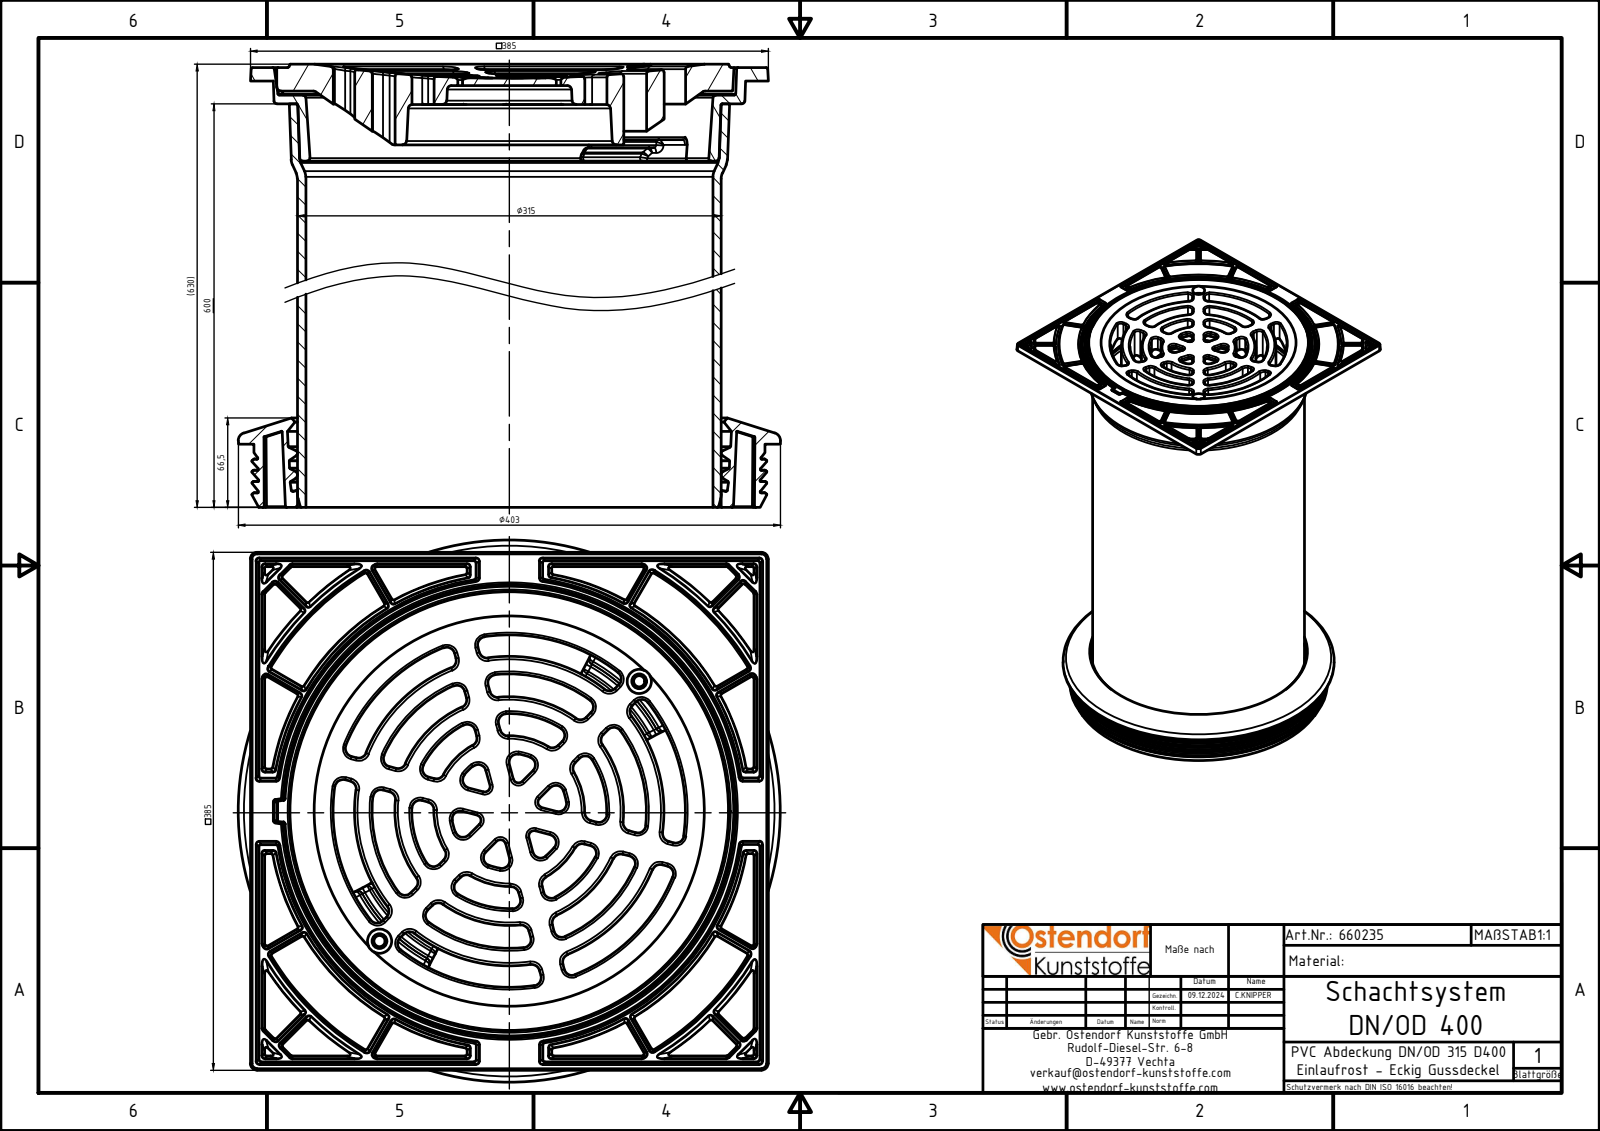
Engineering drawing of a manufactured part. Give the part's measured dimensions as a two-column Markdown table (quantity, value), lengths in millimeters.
| quantity | value |
| --- | --- |
| part name | 660235z; 660300z; 660500z; 990060z (+2 more) |
| STEP written by | Autodesk Inventor 2024 (AUTOMOTIVE_DESIGN) |
| units | millimeters |
| bodies | 4 solids, 1586 faces (235 planar, 431 cylindrical, 920 other) |
| overall size | 629.5 × 403 × 403 |
| volume | 7 698 000 mm³ |
| surface area | 2 173 000 mm² |
| round holes (diameter × count) | 8.38 × 2, 11 × 2, 18 × 2, 302.6 × 1, 315 × 1 |
| round bosses / shafts (diameter × count) | 403 × 1, 380 × 1 |
| partial cylindrical surfaces (radius × count) | 1 × 194, 6 × 84, 2.5 × 48, 4 × 14, 2 × 4, 3 × 1, 43 × 1, 56 × 1 |
| main face-to-face distances | 10, 7.5, 17.5, 2.5, 17, 27, 9.5, 29.5, 20, 12.5 |
| hole center spacings | 136.5, 273 |
